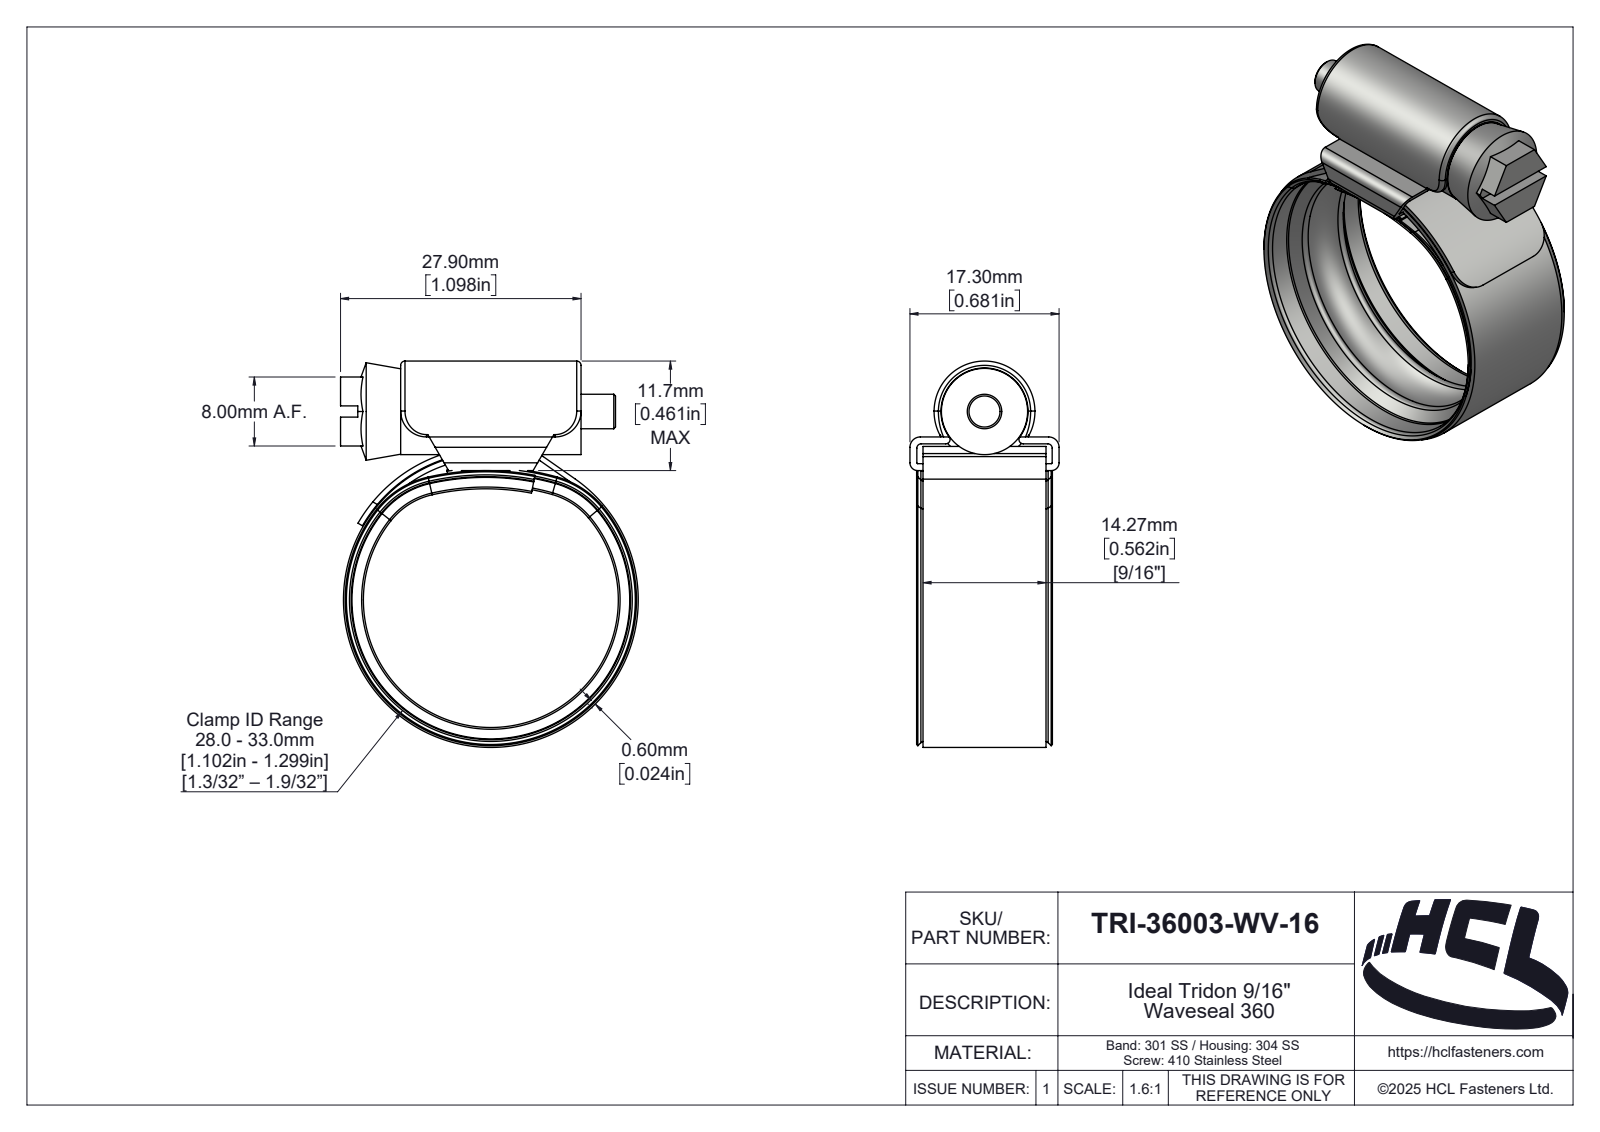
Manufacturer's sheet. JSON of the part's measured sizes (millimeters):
{"part_name": "TRI-36003-WV-16", "step_written_by": "SolidWorks 2025 (AUTOMOTIVE_DESIGN)", "units": "millimeters", "bodies": {"solids": 4, "faces": 418, "planar": 42, "cylindrical": 119, "other": 257}, "overall_size": [44.8, 34.54, 17.3], "volume_mm3": 4298, "surface_area_mm2": 10413, "round_holes": [[33, 1]], "round_bosses_or_shafts": [[34.2, 1], [10, 1], [4, 1]], "partial_cylinders_radius": [[0.5, 6], [3, 4], [0.1, 2], [0.9, 2], [1.2, 2], [9.9, 2], [10.1, 2], [0.46, 1]], "face_to_face_distances": [0.8, 3.1, 2.3, 14.26, 3.9, 0.6, 27.9, 1.52, 15.78, 16.5]}
